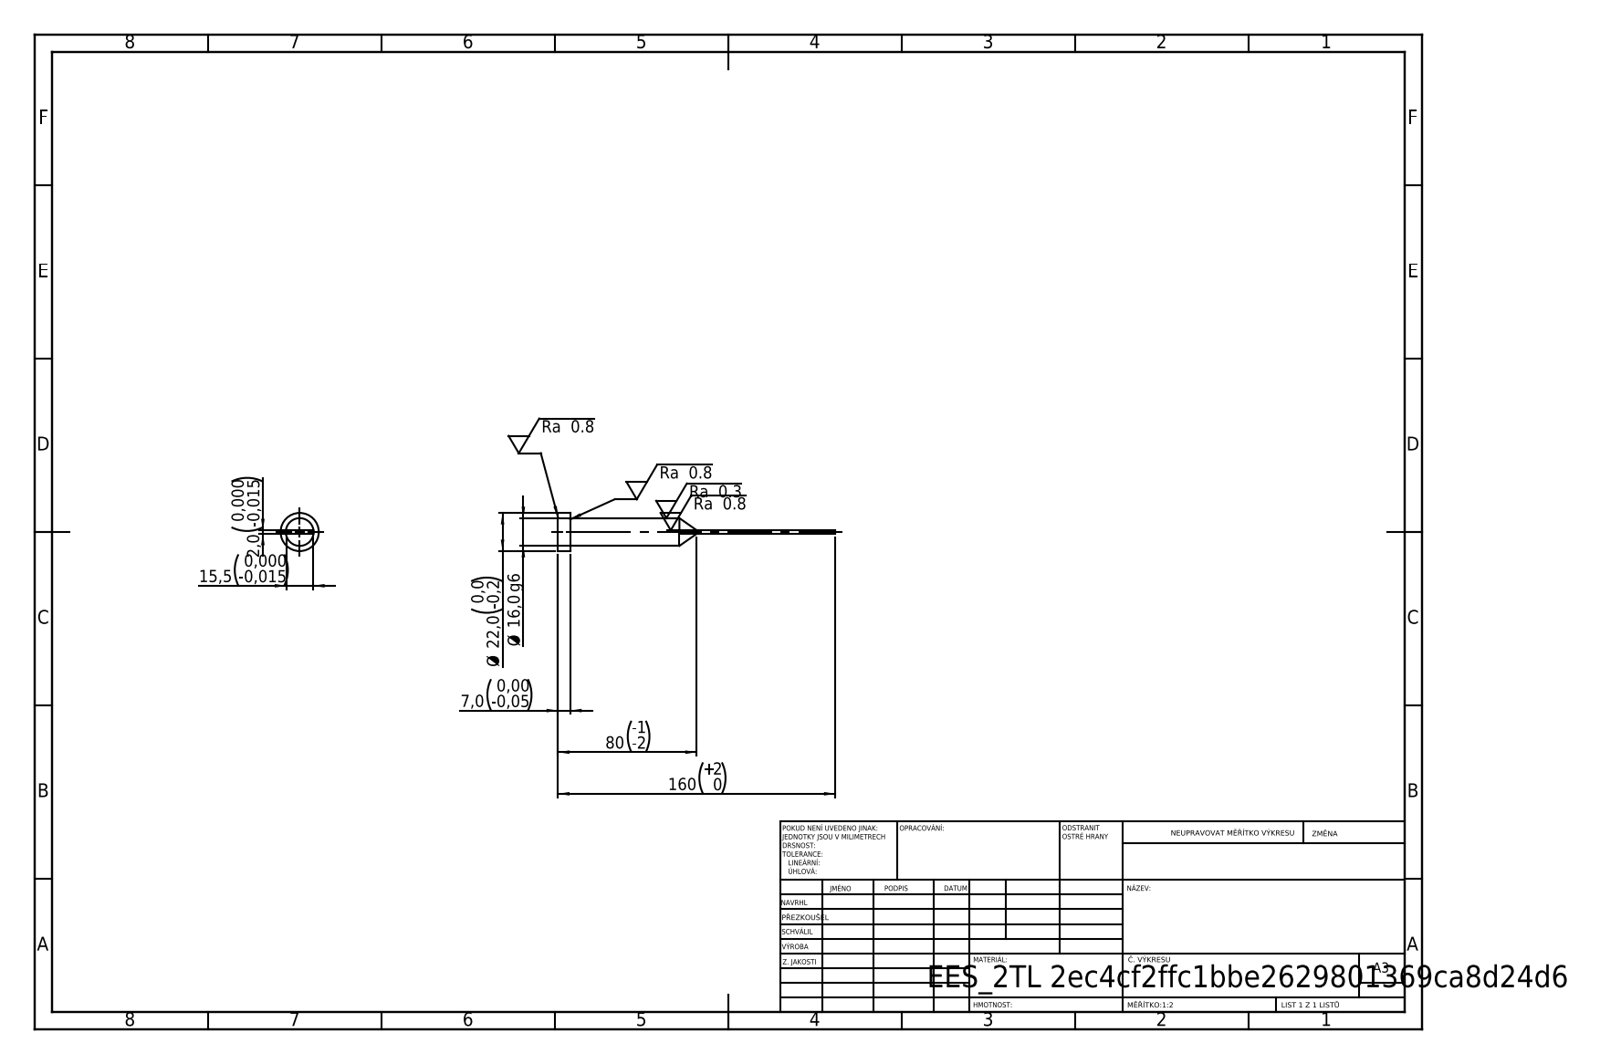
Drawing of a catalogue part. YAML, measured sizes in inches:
step_written_by: "SolidWorks 2019 (CONFIG_CONTROL_DESIGN)"
units: inches
bodies: {solids: 1, faces: 15, planar: 7, cylindrical: 4, other: 4}
overall_size: [6.299, 0.866, 0.866]
volume: 1.153
surface_area: 11.61
round_bosses_or_shafts:
  - {diameter: 0.866, count: 1}
  - {diameter: 0.63, count: 1}
face_to_face_distances: [0.079, 0.276, 0.61, 6.299, 6.024]
